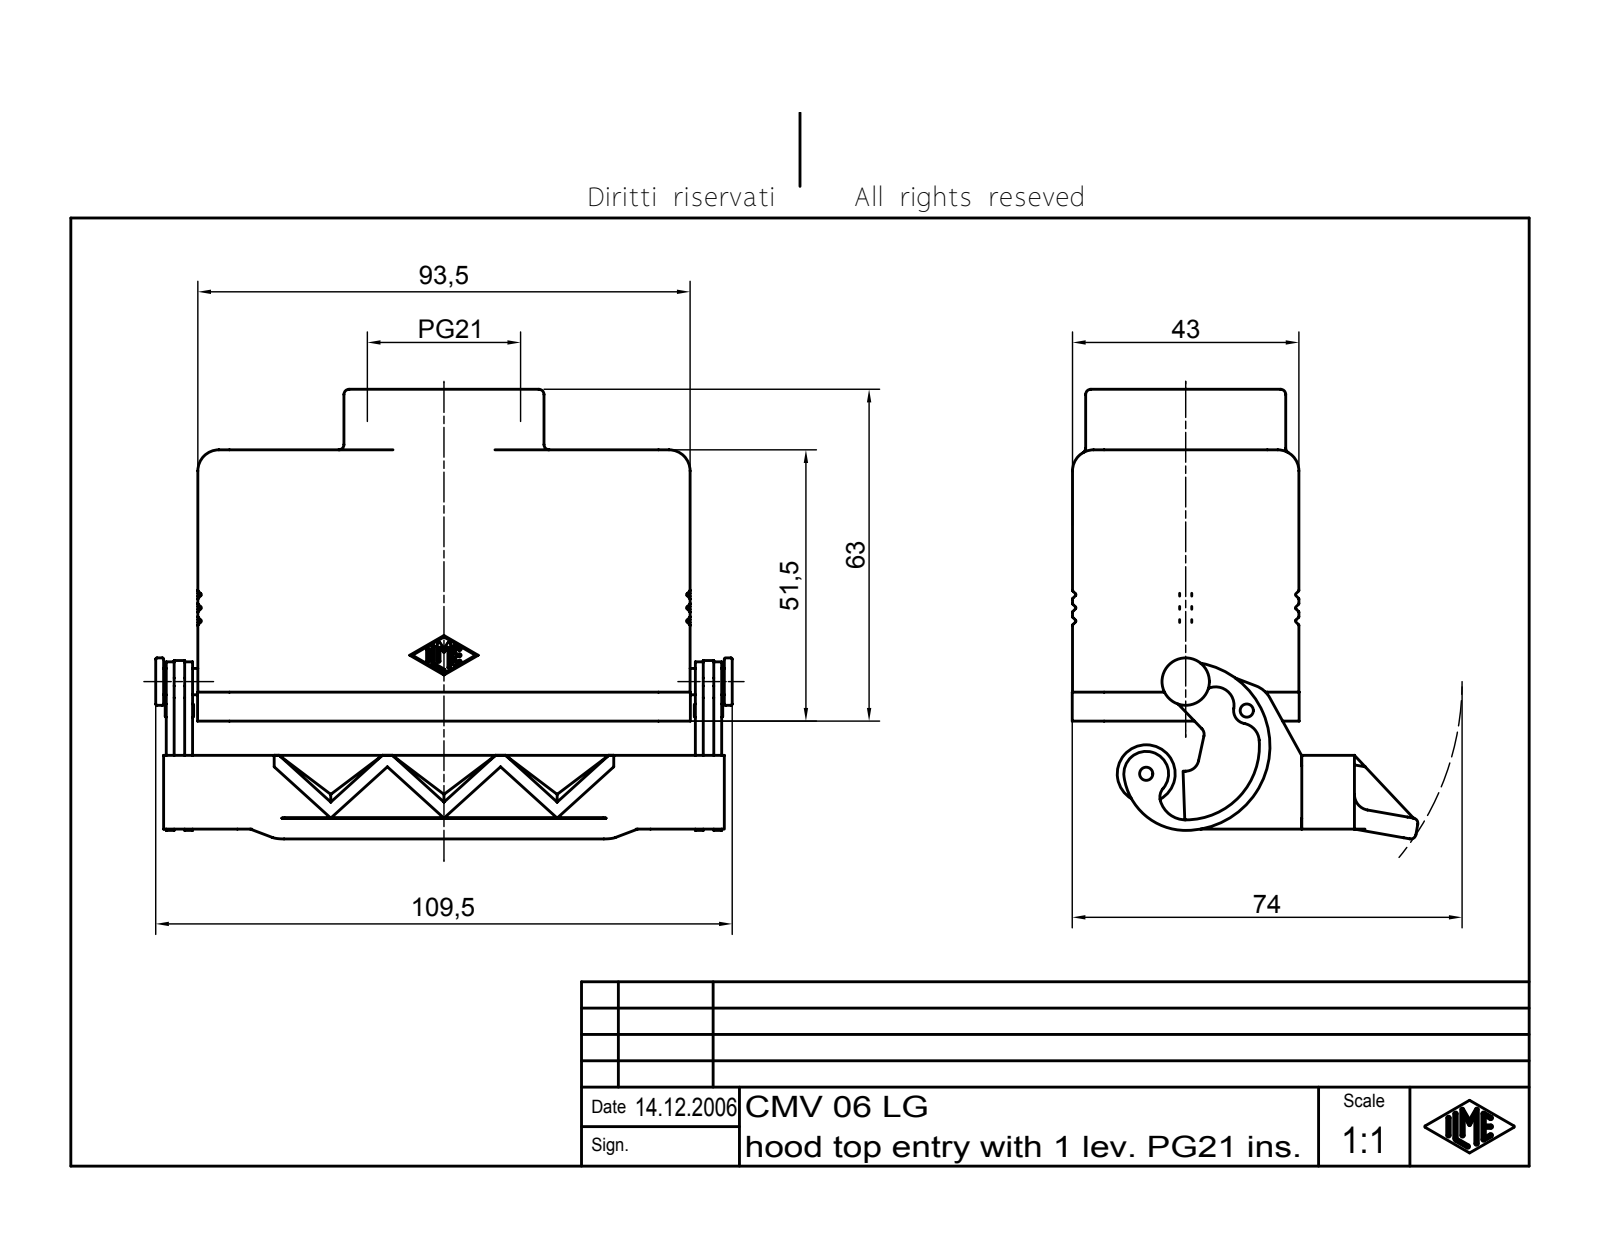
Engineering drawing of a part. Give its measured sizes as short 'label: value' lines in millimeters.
name: CMV 06 LG
written by: Autodesk Inventor 7 (AUTOMOTIVE_DESIGN)
unit: mm
bodies: 1 solid, 779 faces (176 planar, 283 cylindrical, 320 other)
size: 109.5 × 85.37 × 65.64
volume: 85 986 mm³; area: 46 664 mm²
holes: 1× ⌀2.5, 1× ⌀24.78, 1× ⌀26.78
bosses: 1× ⌀38, 1× ⌀11, 1× ⌀9, 1× ⌀5, 1× ⌀3.1, 1× ⌀2
rounds: 52× R0.2, 23× R0.25, 9× R2.5, 6× R1, 5× R4, 4× R2.45, 4× R6, 4× R6.05
face distances: 3.5, 39.5, 36, 43, 3.55, 90, 4.5, 3.6, 93.5, 8
